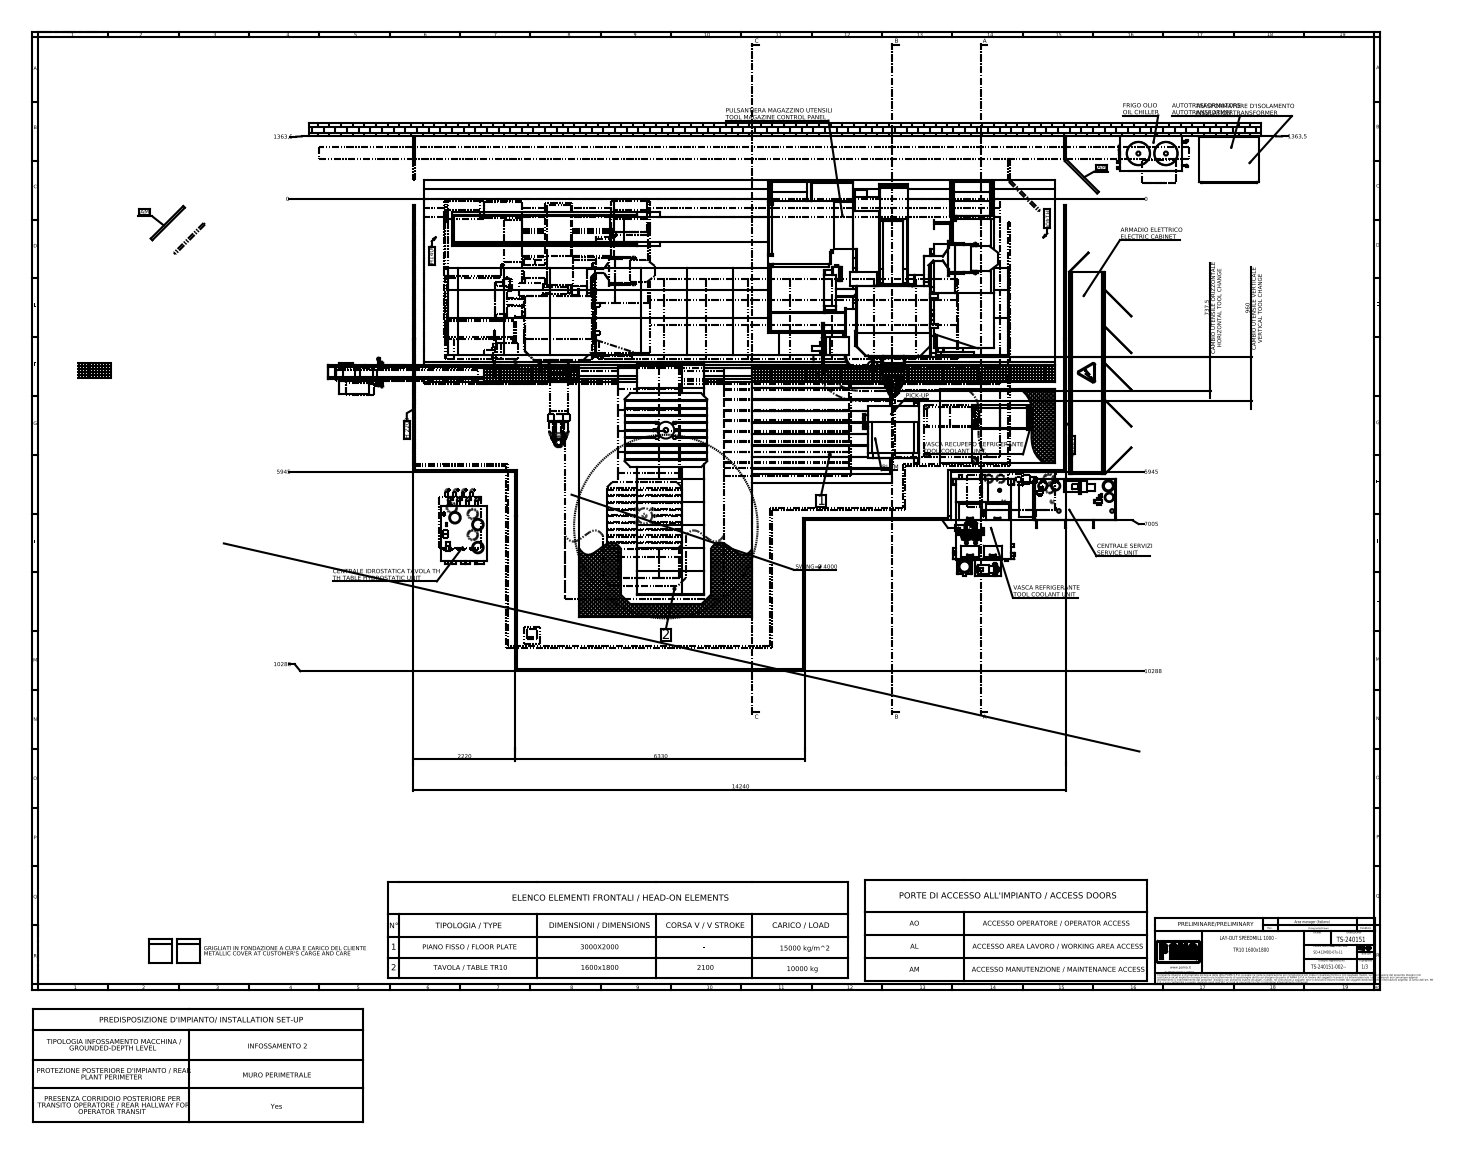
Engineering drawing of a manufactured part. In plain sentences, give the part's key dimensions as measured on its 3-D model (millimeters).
The part is named "S003543_Y=2500; S002770_L=9000; S002835_X=7000; S000885_L=895 (+8 more)". Its 3-D file was written by "SolidWorks 2023 (AUTOMOTIVE_DESIGN)". It is 447 solids with 7416 faces: 5229 planar, 1585 cylindrical and 602 other. Overall it measures 24197.11 by 14901.5 by 9400 millimeters. Its volume is 624 100 000 000 cubic millimeters and its surface area 1 966 000 000 square millimeters. Round holes: 90 of diameter 35, 63 of diameter 69.6, 8 of diameter 13, 8 of diameter 14, 6 of diameter 8, 6 of diameter 32, 4 of diameter 12.5, 3 of diameter 50, 3 of diameter 56.66, 2 of diameter 4.2, 2 of diameter 19, 2 of diameter 30. Round bosses or shafts: 14 of diameter 20, 10 of diameter 9, 8 of diameter 30, 7 of diameter 66.3, 7 of diameter 60, 6 of diameter 35, 4 of diameter 200, 4 of diameter 170. Partial cylindrical surfaces (rounded edges, fillets, slot ends): 166 of radius 5, 46 of radius 15, 41 of radius 6, 27 of radius 10, 26 of radius 35, 20 of radius 3, 20 of radius 20, 18 of radius 8. The main face-to-face distances are 2000, 300, 50, 1340, 660, 14901.5, 14601.5, 20740, 150, 100. The hole center spacings are 250, 500, 750, 1000, 1250, 1500, 1750, 2000.
